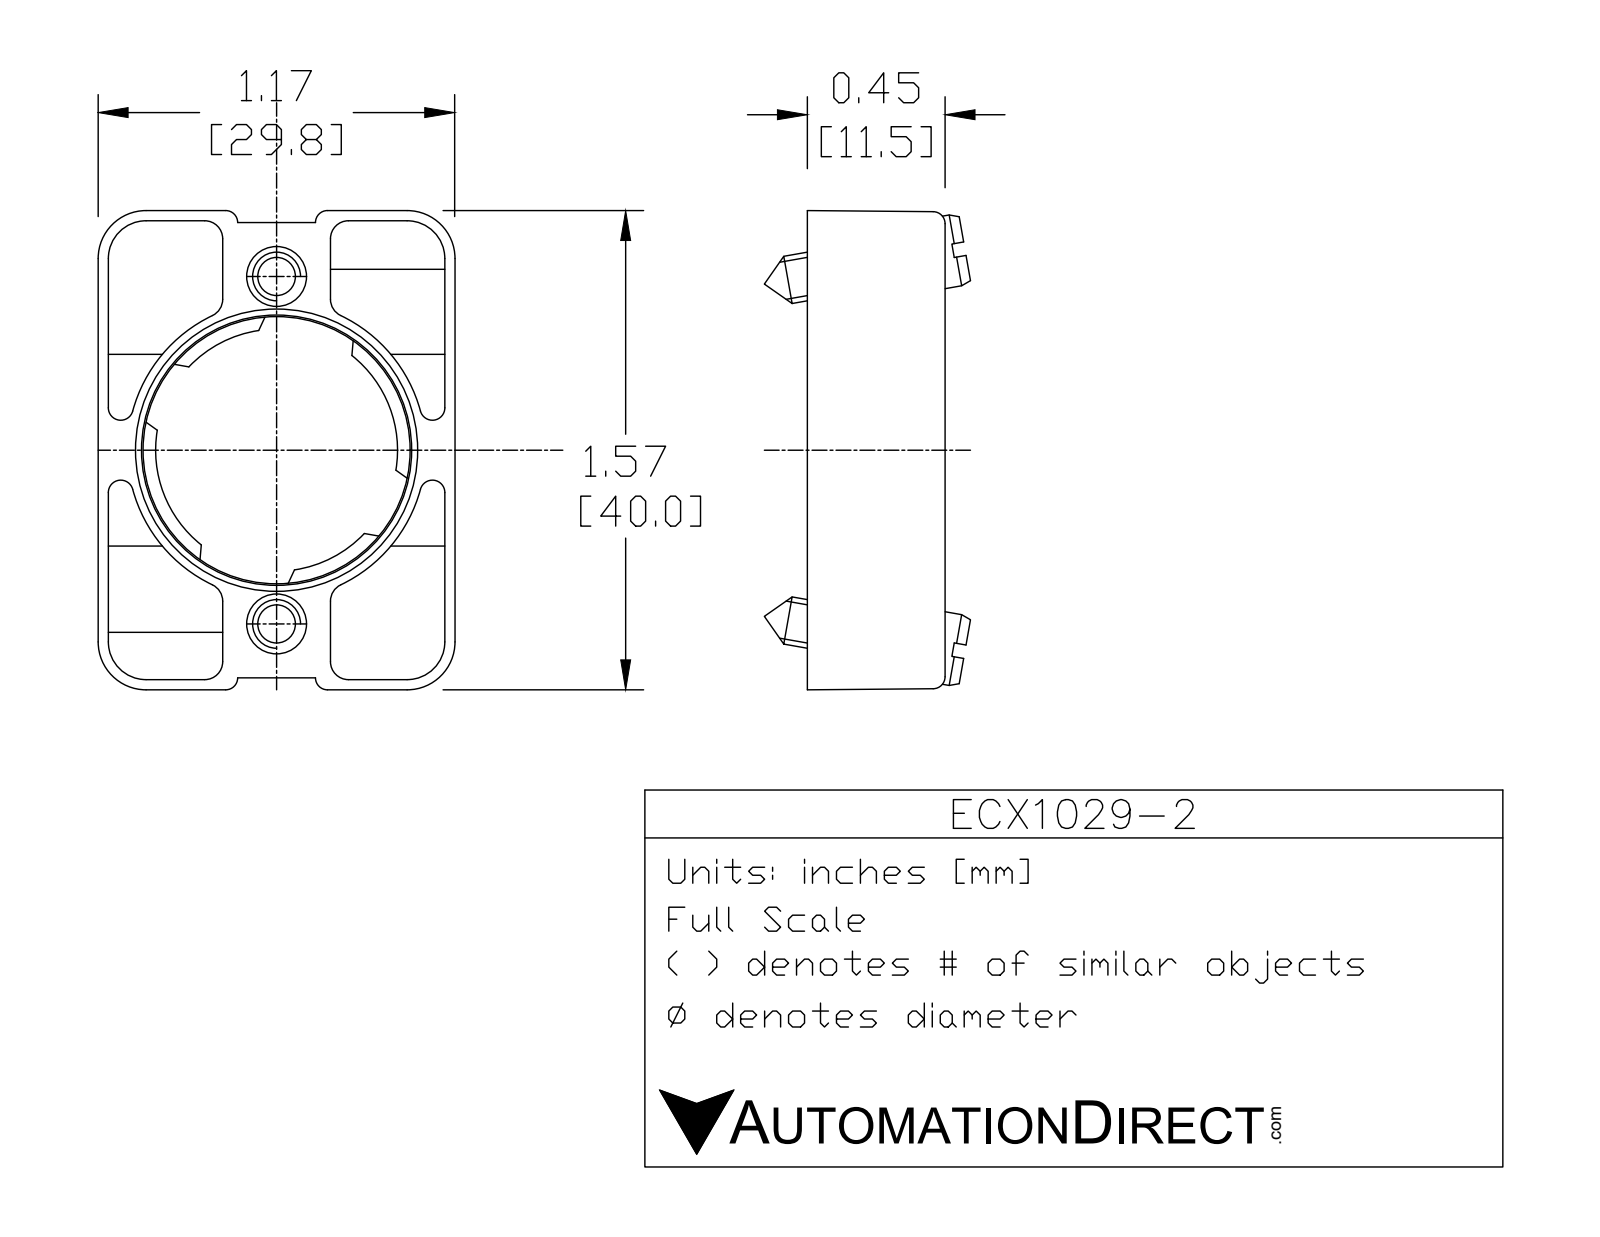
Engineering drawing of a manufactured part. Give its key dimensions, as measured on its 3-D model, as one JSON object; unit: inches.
{"part_name": "ECX1029-2", "step_written_by": "SolidWorks 2016 (AUTOMOTIVE_DESIGN)", "units": "inches", "bodies": {"solids": 3, "faces": 235, "planar": 122, "cylindrical": 97, "other": 16}, "overall_size": [1.581, 1.178, 0.834], "volume_in3": 0.253, "surface_area_in2": 10.28, "round_holes": [[0.124, 2], [0.13, 2], [0.197, 1], [0.878, 1], [0.888, 1]], "round_bosses_or_shafts": [[0.157, 2]], "partial_cylinders_radius": [[0.059, 24], [0.041, 12], [0.124, 12], [0.157, 12], [0.039, 4], [0.128, 2], [0.398, 1], [0.49, 1]], "face_to_face_distances": [0.033, 0.031, 1.143, 1.142, 1.144, 0.435, 0.404, 1.141, 1.541, 1.175]}
